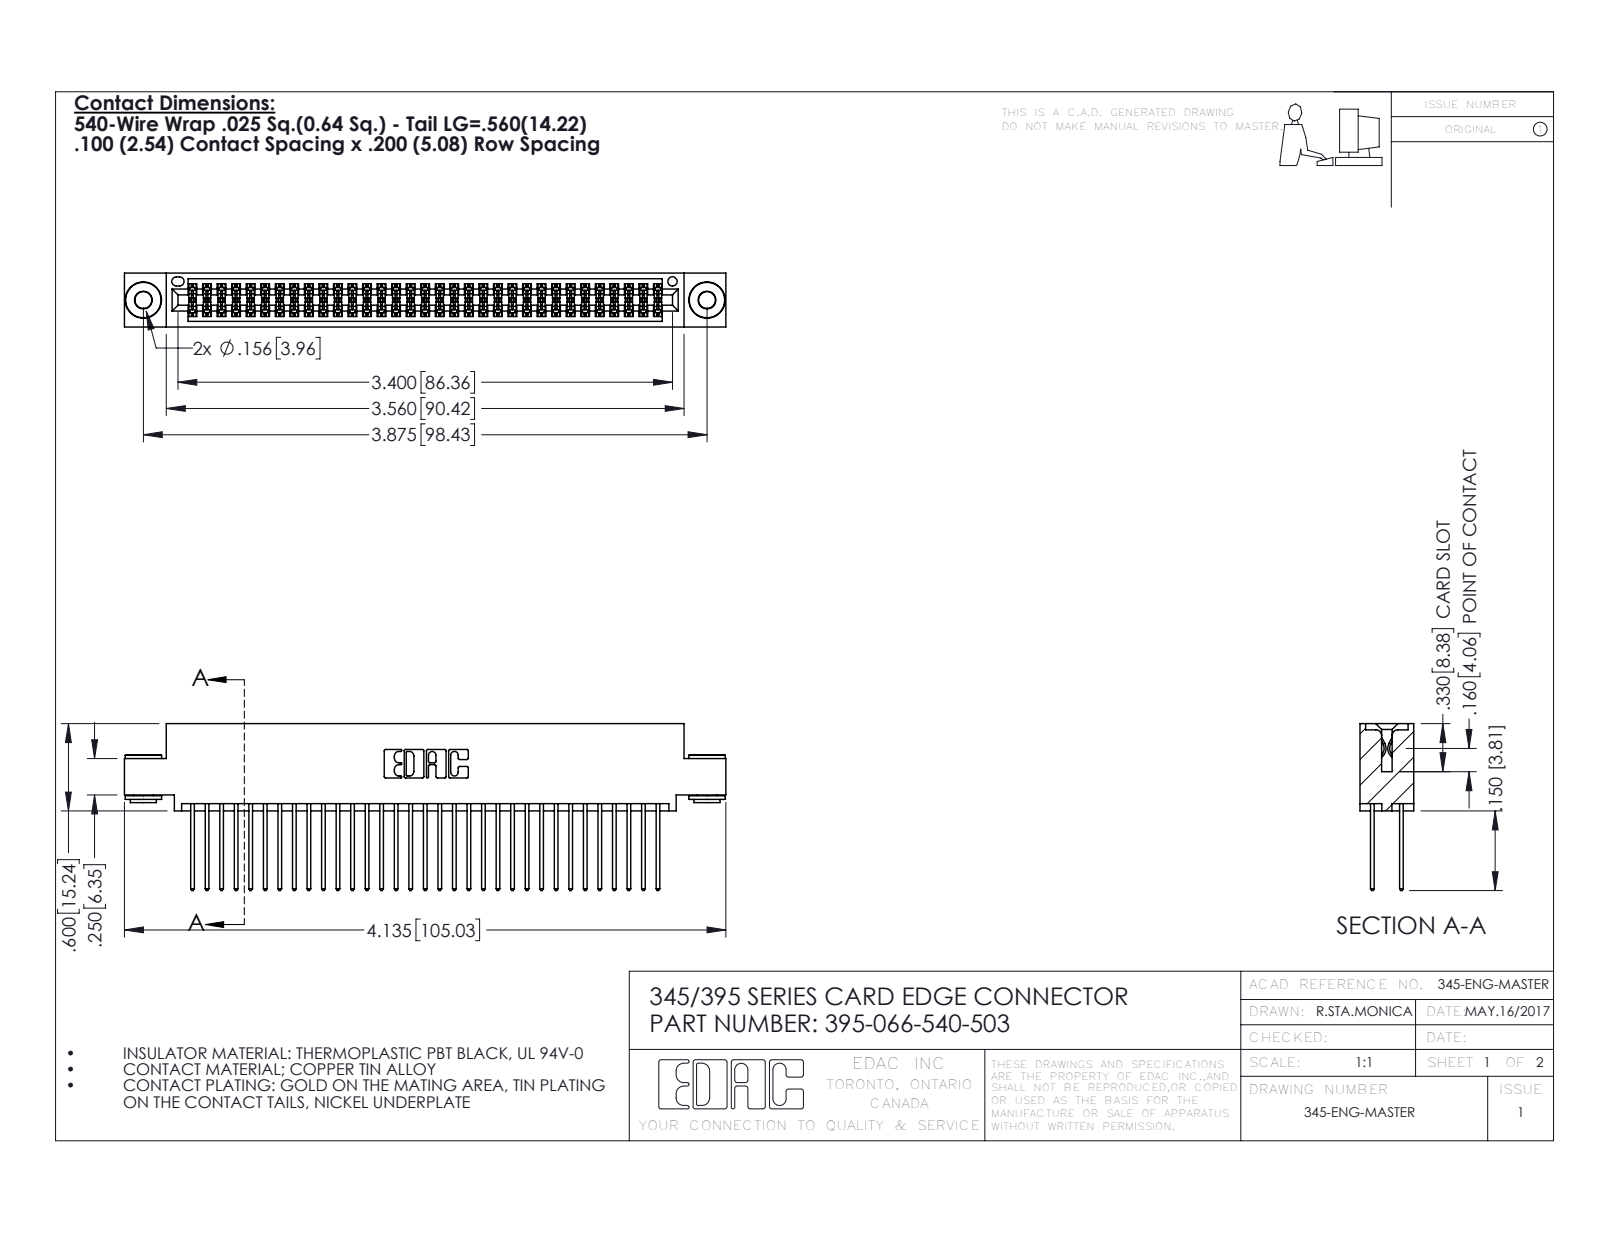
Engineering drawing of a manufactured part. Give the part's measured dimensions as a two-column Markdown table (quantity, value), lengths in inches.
| quantity | value |
| --- | --- |
| part name | 395-066-540-503; 345 Part_0.110 Offset - 0.156 Dia-TH; 345-250-002_345-250-002-102; 345-292-001_345-293-140 |
| STEP written by | SolidWorks 2016 (CONFIG_CONTROL_DESIGN) |
| units | inches |
| bodies | 69 solids, 3468 faces (2272 planar, 1188 cylindrical, 8 other) |
| overall size | 4.135 × 1.147 × 0.37 |
| volume | 0.629 in³ |
| surface area | 25.62 in² |
| round holes (diameter × count) | 0.116 × 2, 0.156 × 2, 0.064 × 1 |
| round bosses / shafts (diameter × count) | 0.25 × 2, 0.18 × 2, 0.136 × 2 |
| partial cylindrical surfaces (radius × count) | 0.006 × 99, 0.01 × 66, 0.01 × 22, 0.007 × 6, 0.031 × 6, 0.026 × 3, 0.014 × 2, 0.019 × 2 |
| main face-to-face distances | 0.072, 0.298, 0.2, 0.025, 0.098, 0.272, 0.37, 0.225, 0.175, 0.149 |
| hole center spacings | 0.27, 3.64, 3.875 |
